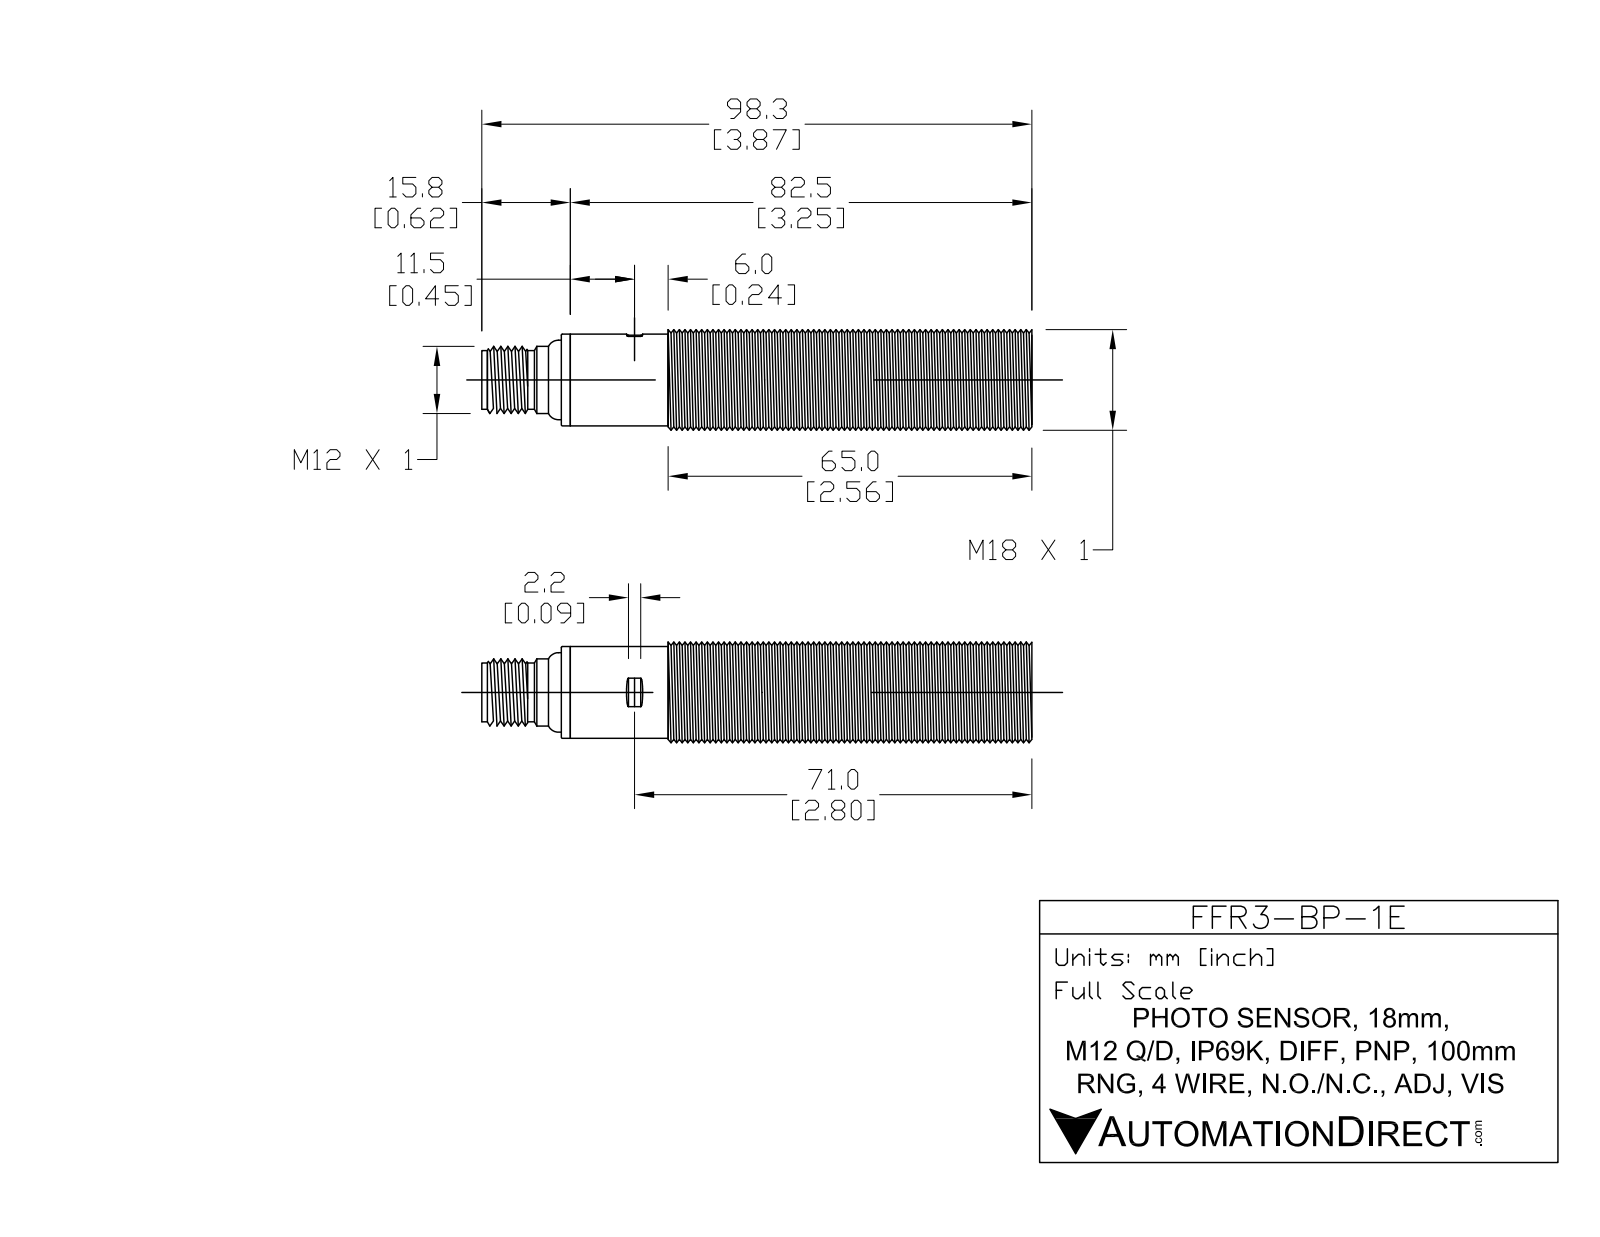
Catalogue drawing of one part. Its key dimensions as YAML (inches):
part_name: "FFR3-BP-1E"
step_written_by: "SolidWorks 2017 (AUTOMOTIVE_DESIGN)"
units: inches
bodies: {solids: 5, faces: 118, planar: 21, cylindrical: 48, other: 49}
overall_size: [3.268, 0.709, 0.709]
volume: 1.081
surface_area: 10.47
round_holes:
  - {diameter: 0.278, count: 1}
  - {diameter: 0.327, count: 1}
  - {diameter: 0.5, count: 1}
  - {diameter: 0.583, count: 1}
  - {diameter: 0.61, count: 1}
round_bosses_or_shafts:
  - {diameter: 0.039, count: 4}
  - {diameter: 0.709, count: 1}
  - {diameter: 0.646, count: 1}
  - {diameter: 0.612, count: 1}
  - {diameter: 0.604, count: 1}
  - {diameter: 0.559, count: 1}
  - {diameter: 0.492, count: 1}
  - {diameter: 0.472, count: 1}
partial_cylinders:
  - {radius: 0.024, count: 1}
  - {radius: 0.63, count: 1}
face_to_face_distances: [2.539, 0.118, 2.657, 0.024, 0.094, 2.634, 2.717, 2.693, 2.598, 0.059]
